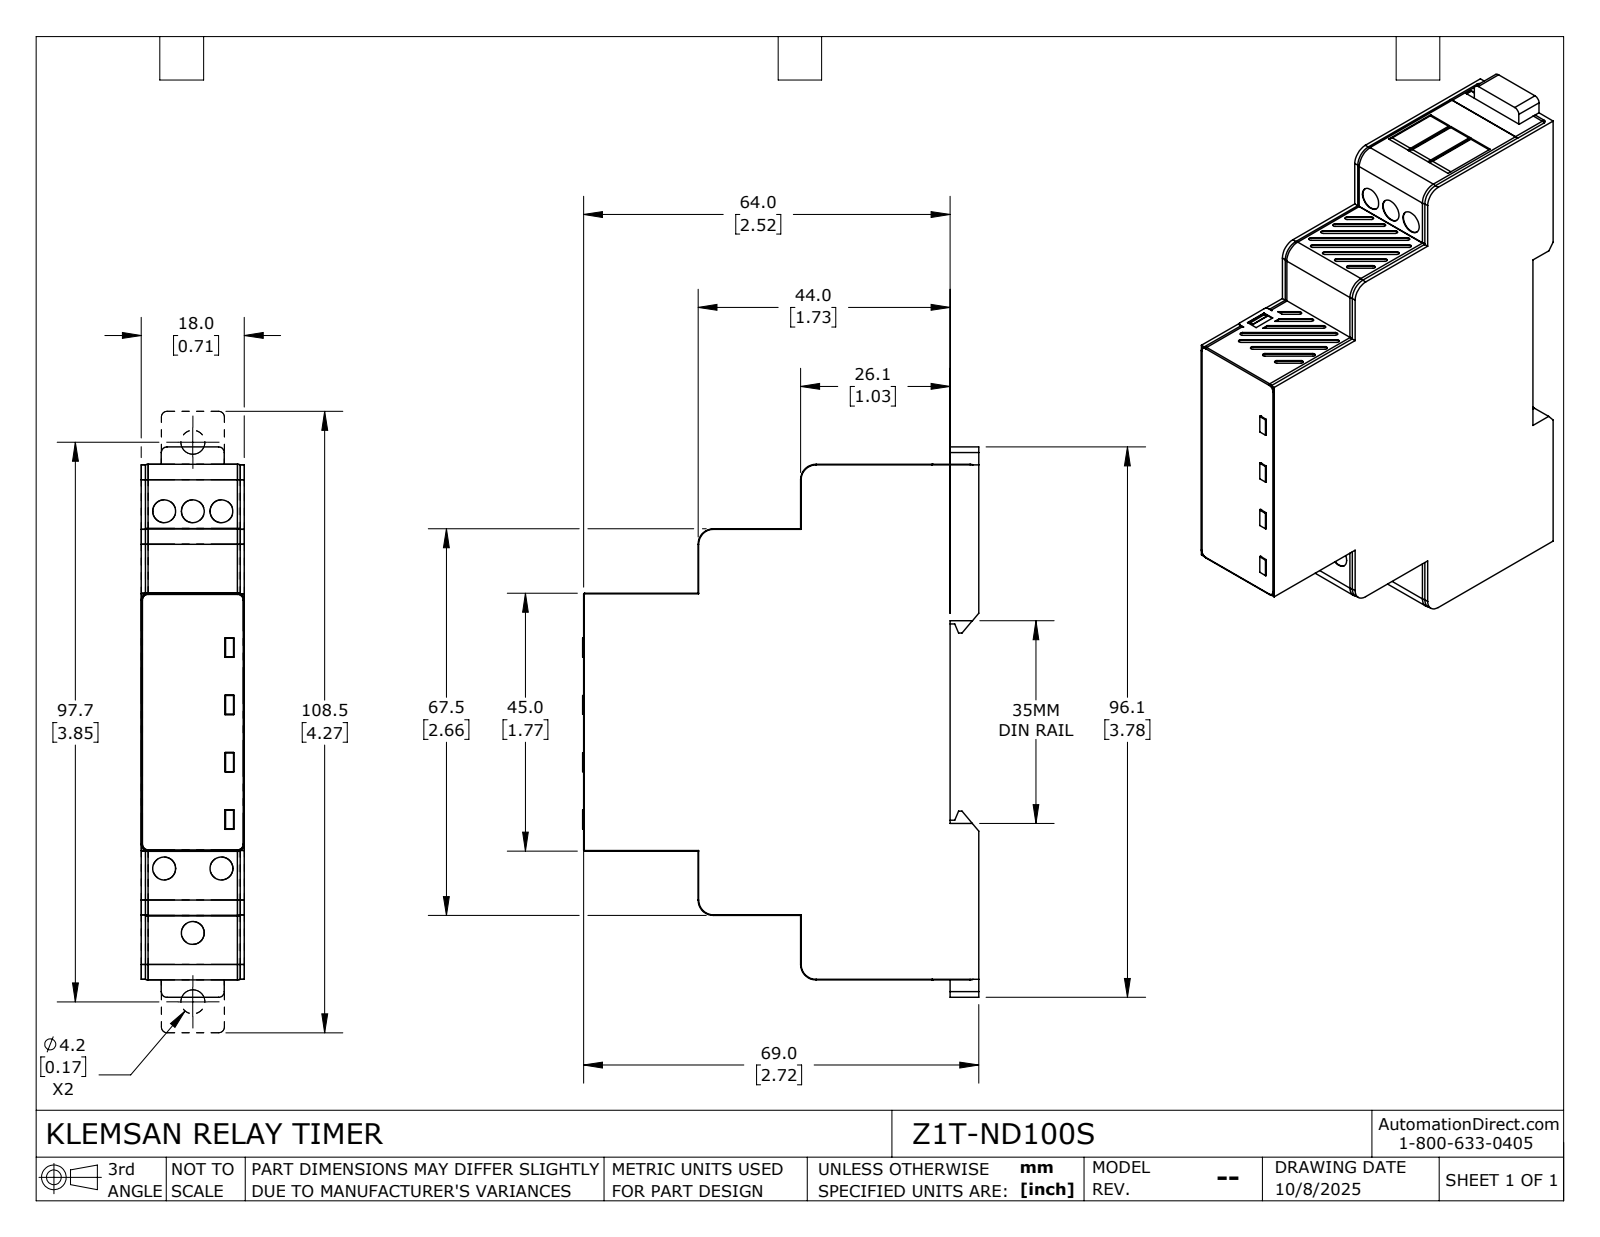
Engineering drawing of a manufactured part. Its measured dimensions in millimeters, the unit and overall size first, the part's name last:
Units: millimetres
Overall size (bounding box): 96.07 × 69.15 × 18
Round holes (diameter × count): ⌀4.2 ×2, ⌀4 ×1
Partial cylindrical surfaces — rounded edges, fillets, slot ends (radius × count): R1.2 ×16, R0.2 ×4, R1 ×4, R2.6 ×4, R2.7 ×4, R0.5 ×2, R1.5 ×2
Main face-to-face distances: 18, 3.5, 14.5, 11.25, 64, 5, 69, 22.5, 67.4, 67.5
Hole centre spacings: 5.83, 79.43, 85.26
Volume: 83 847 mm³ · Surface area: 17 884 mm²
Bodies: 3 solids, 440 faces (280 planar, 60 cylindrical, 100 other)
Part name (STEP PRODUCT): Z1T-ND100S
STEP written by: SolidWorks 2024 (CONFIG_CONTROL_DESIGN)
